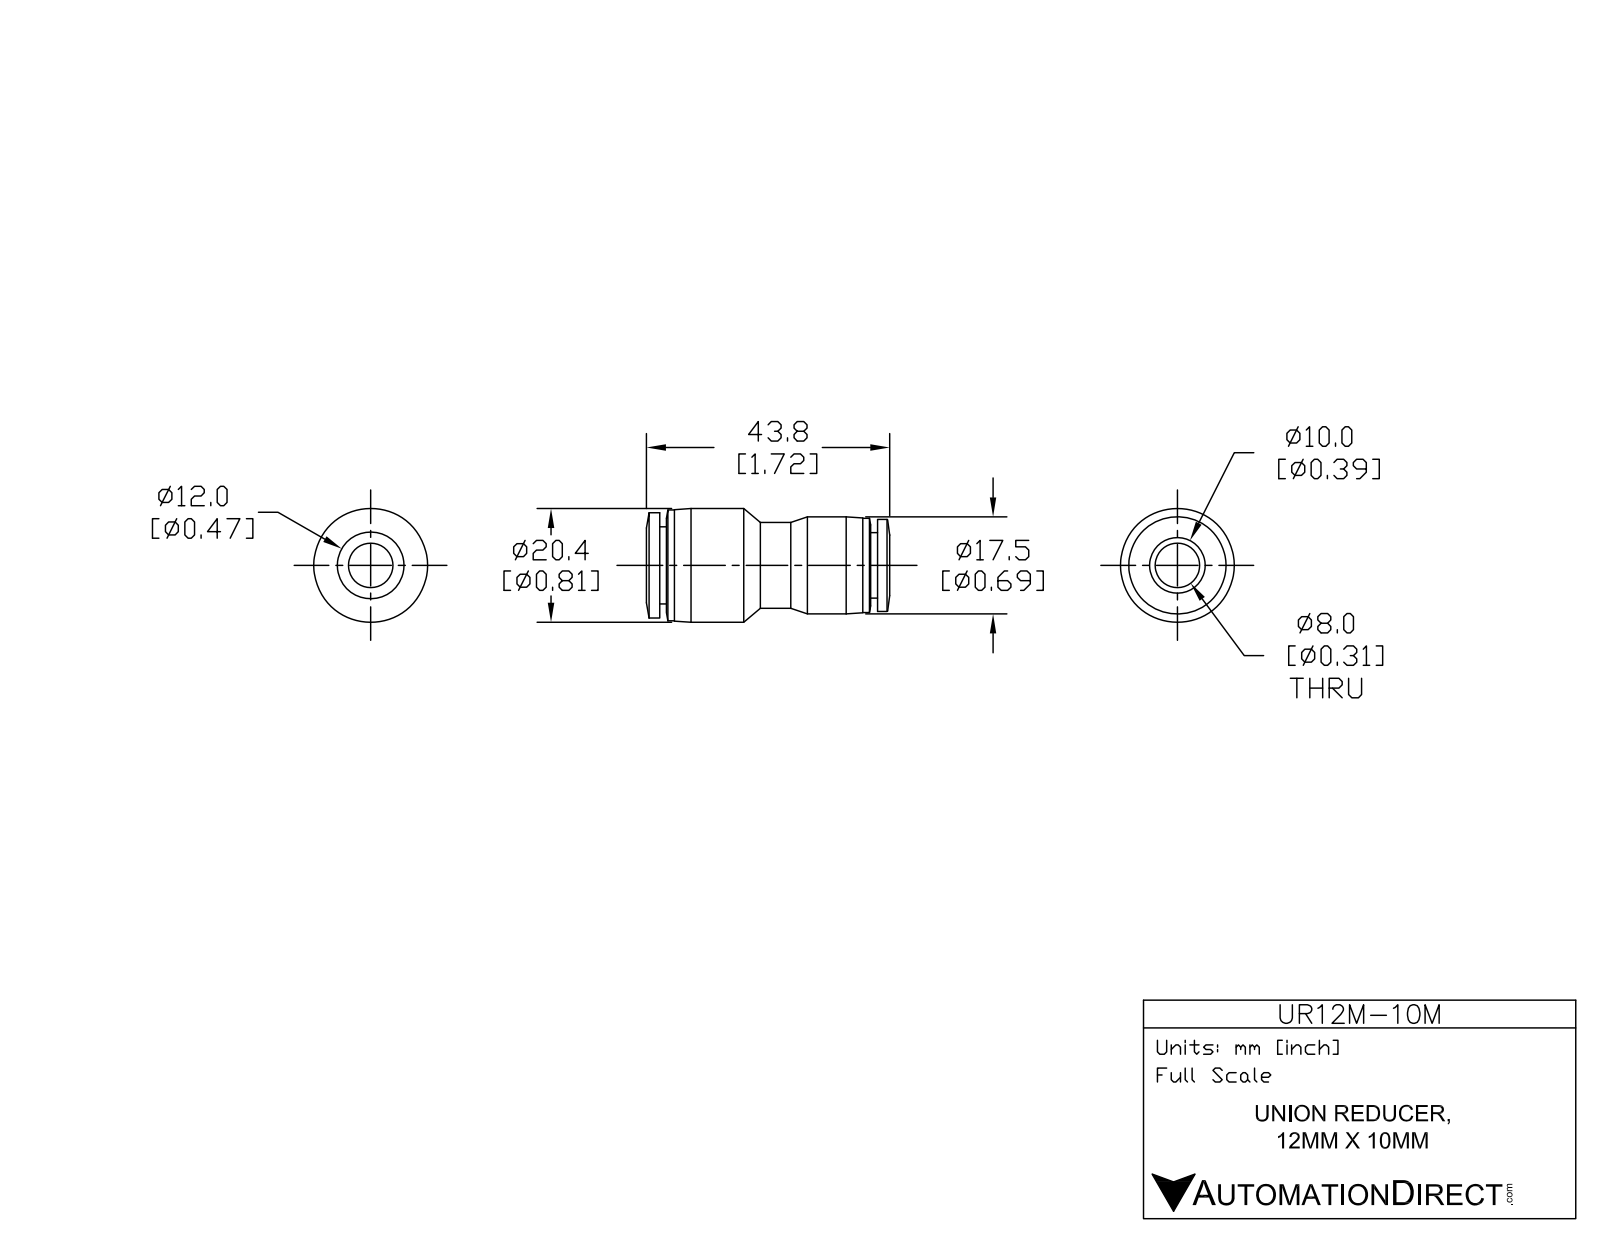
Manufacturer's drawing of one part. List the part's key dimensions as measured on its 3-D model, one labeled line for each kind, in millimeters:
Part name (STEP PRODUCT): UR12M-10M
STEP written by: SolidWorks 2015 (AUTOMOTIVE_DESIGN)
Units: millimetres
Bodies: 1 solid, 56 faces (10 planar, 24 cylindrical, 22 other)
Overall size (bounding box): 43.9 × 20.5 × 20.5
Volume: 6 670 mm³ · Surface area: 4 927 mm²
Round holes (diameter × count): ⌀8 ×1, ⌀10.3 ×1, ⌀12.3 ×1
Round bosses / shafts (diameter × count): ⌀20.5 ×1, ⌀20 ×1, ⌀19 ×1, ⌀17.5 ×1, ⌀17 ×1, ⌀16.6 ×1, ⌀15.5 ×1, ⌀13.9 ×1
Main face-to-face distances: 39.3, 38.1, 1.2, 18.8, 19.3, 20.5, 1.2, 17.6, 36.9, 38
